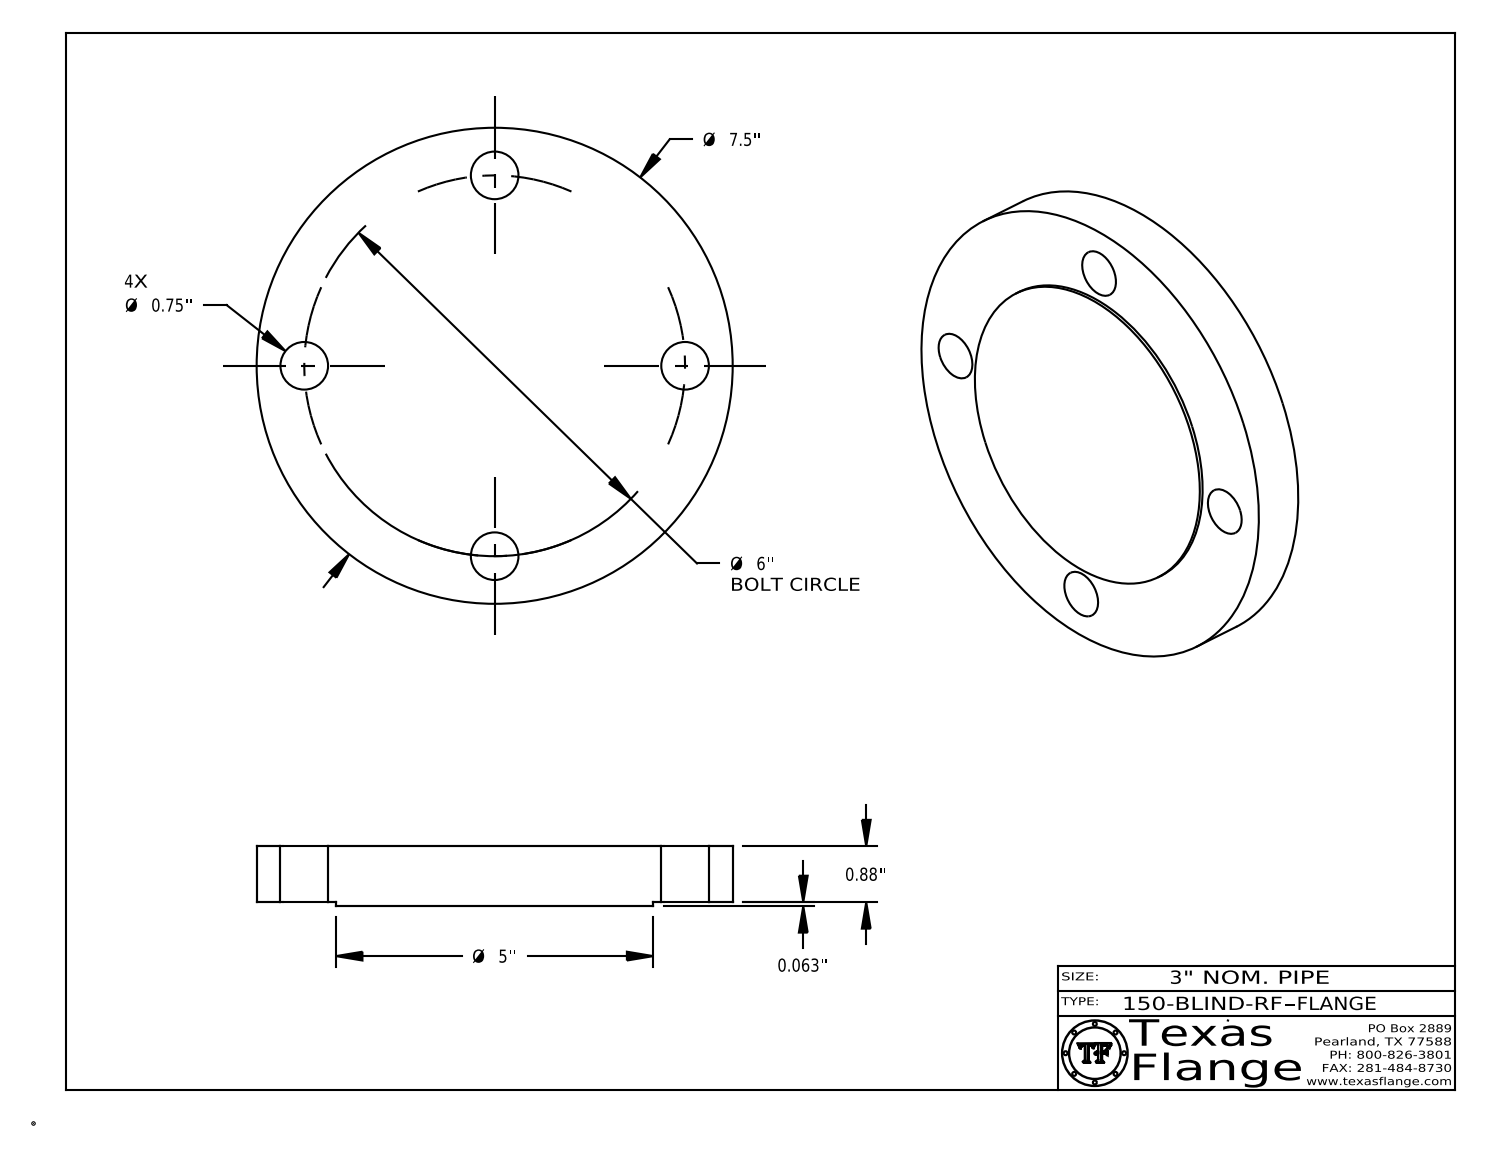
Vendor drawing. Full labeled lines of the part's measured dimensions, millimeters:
Part name (STEP PRODUCT): 150-BLIND-RF
STEP written by: CATIA V5 STEP AP214 (AUTOMOTIVE_DESIGN)
Units: millimetres
Bodies: 1 solid, 400 faces (368 planar, 32 cylindrical, 0 other)
Overall size (bounding box): 190.5 × 190.5 × 24
Volume: 631 700 mm³ · Surface area: 74 130 mm²
Round holes (diameter × count): ⌀19.1 ×4, ⌀12.6 ×1
Round bosses / shafts (diameter × count): ⌀0.8 ×8, ⌀190.5 ×1, ⌀127 ×1, ⌀9.9 ×1
Main face-to-face distances: 22.4, 1.6, 24, 23.6, 22, 0.4, 3.8, 3.7, 0.7, 3.1
Hole centre spacings: 107.8, 58.3, 140.8, 152.4
